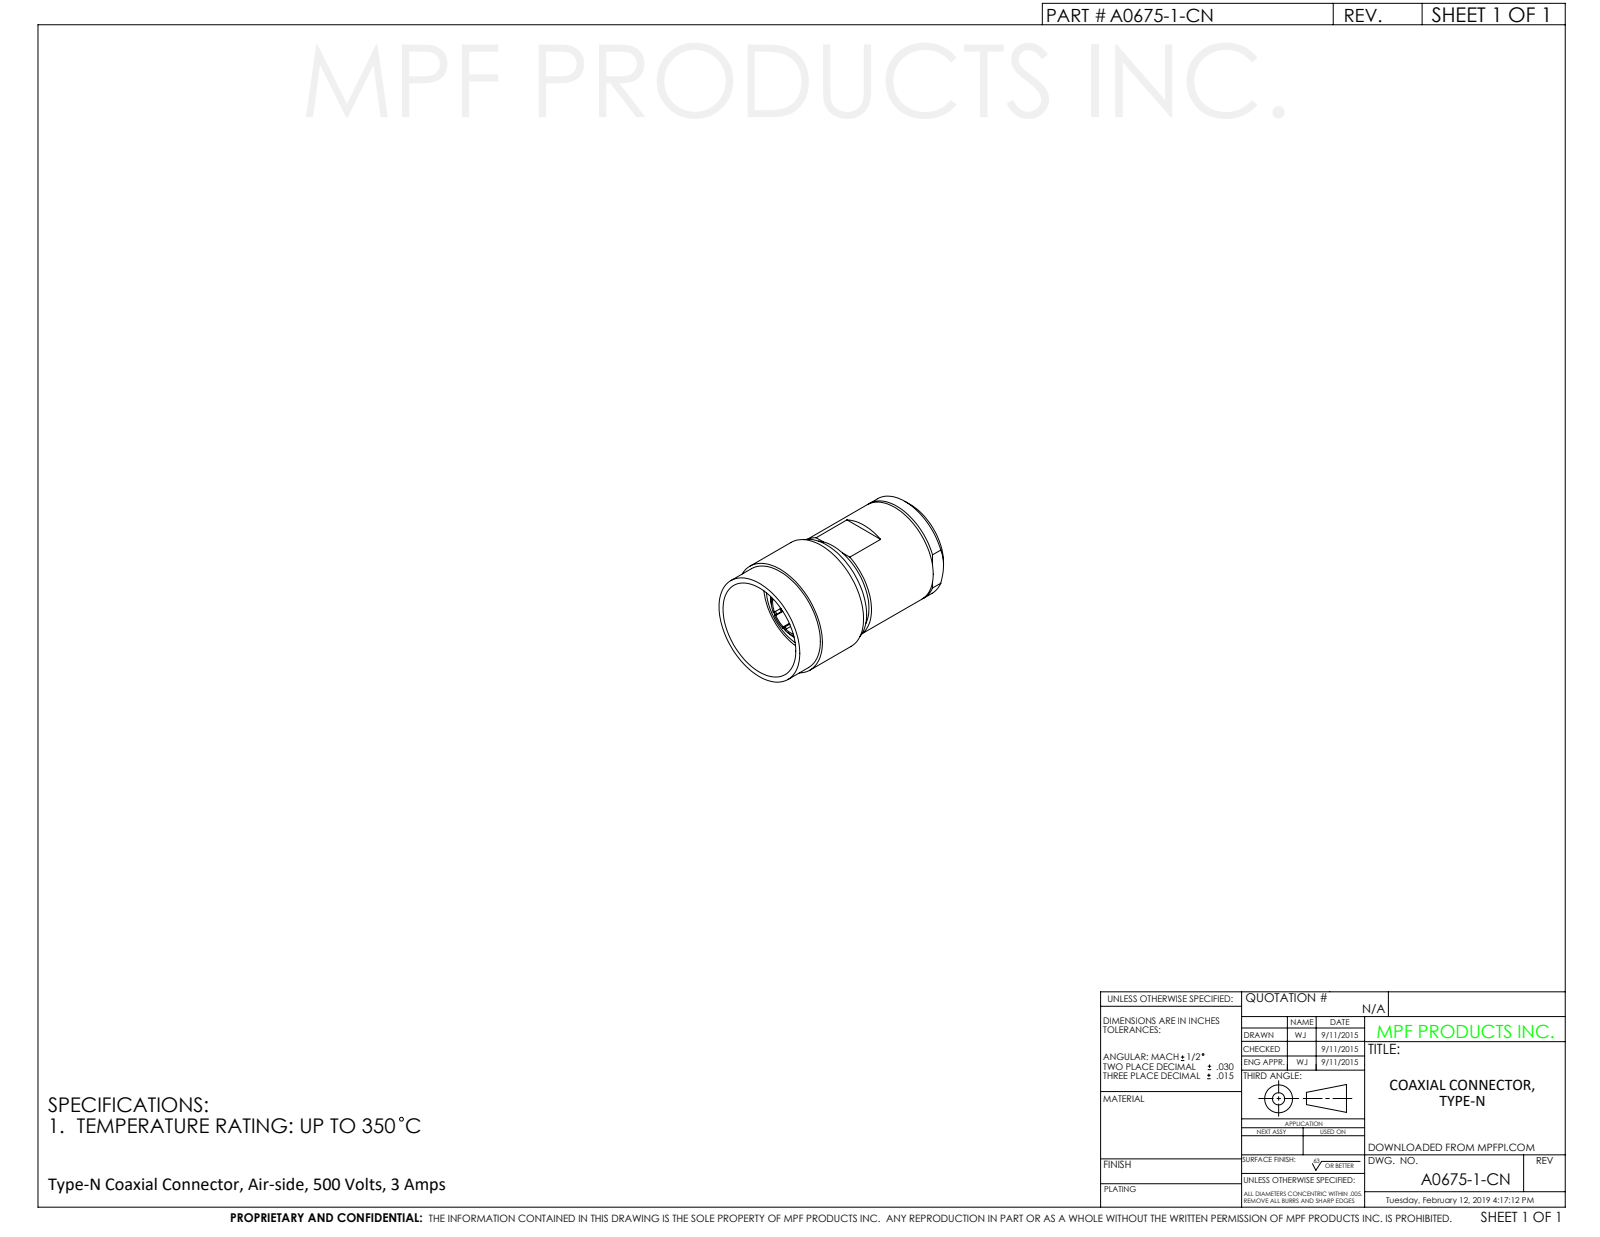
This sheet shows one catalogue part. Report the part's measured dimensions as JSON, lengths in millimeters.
{"part_name": "A0675-1-CN", "step_written_by": "SolidWorks 2012 (CONFIG_CONTROL_DESIGN)", "units": "millimeters", "bodies": {"solids": 1, "faces": 107, "planar": 67, "cylindrical": 34, "other": 6}, "overall_size": [37.2, 21, 21], "volume_mm3": 8360, "surface_area_mm2": 4179, "round_holes": [[8.8, 1], [10.2, 1], [18, 1]], "round_bosses_or_shafts": [[21, 1], [19.9, 1], [19.1, 1], [17.8, 1], [16, 1], [15.7, 1], [12, 1], [9.5, 1]], "face_to_face_distances": [27.6, 3.8, 23.8, 3.3, 0.5, 24.3, 20.7, 17.4, 16.9, 6.9]}
